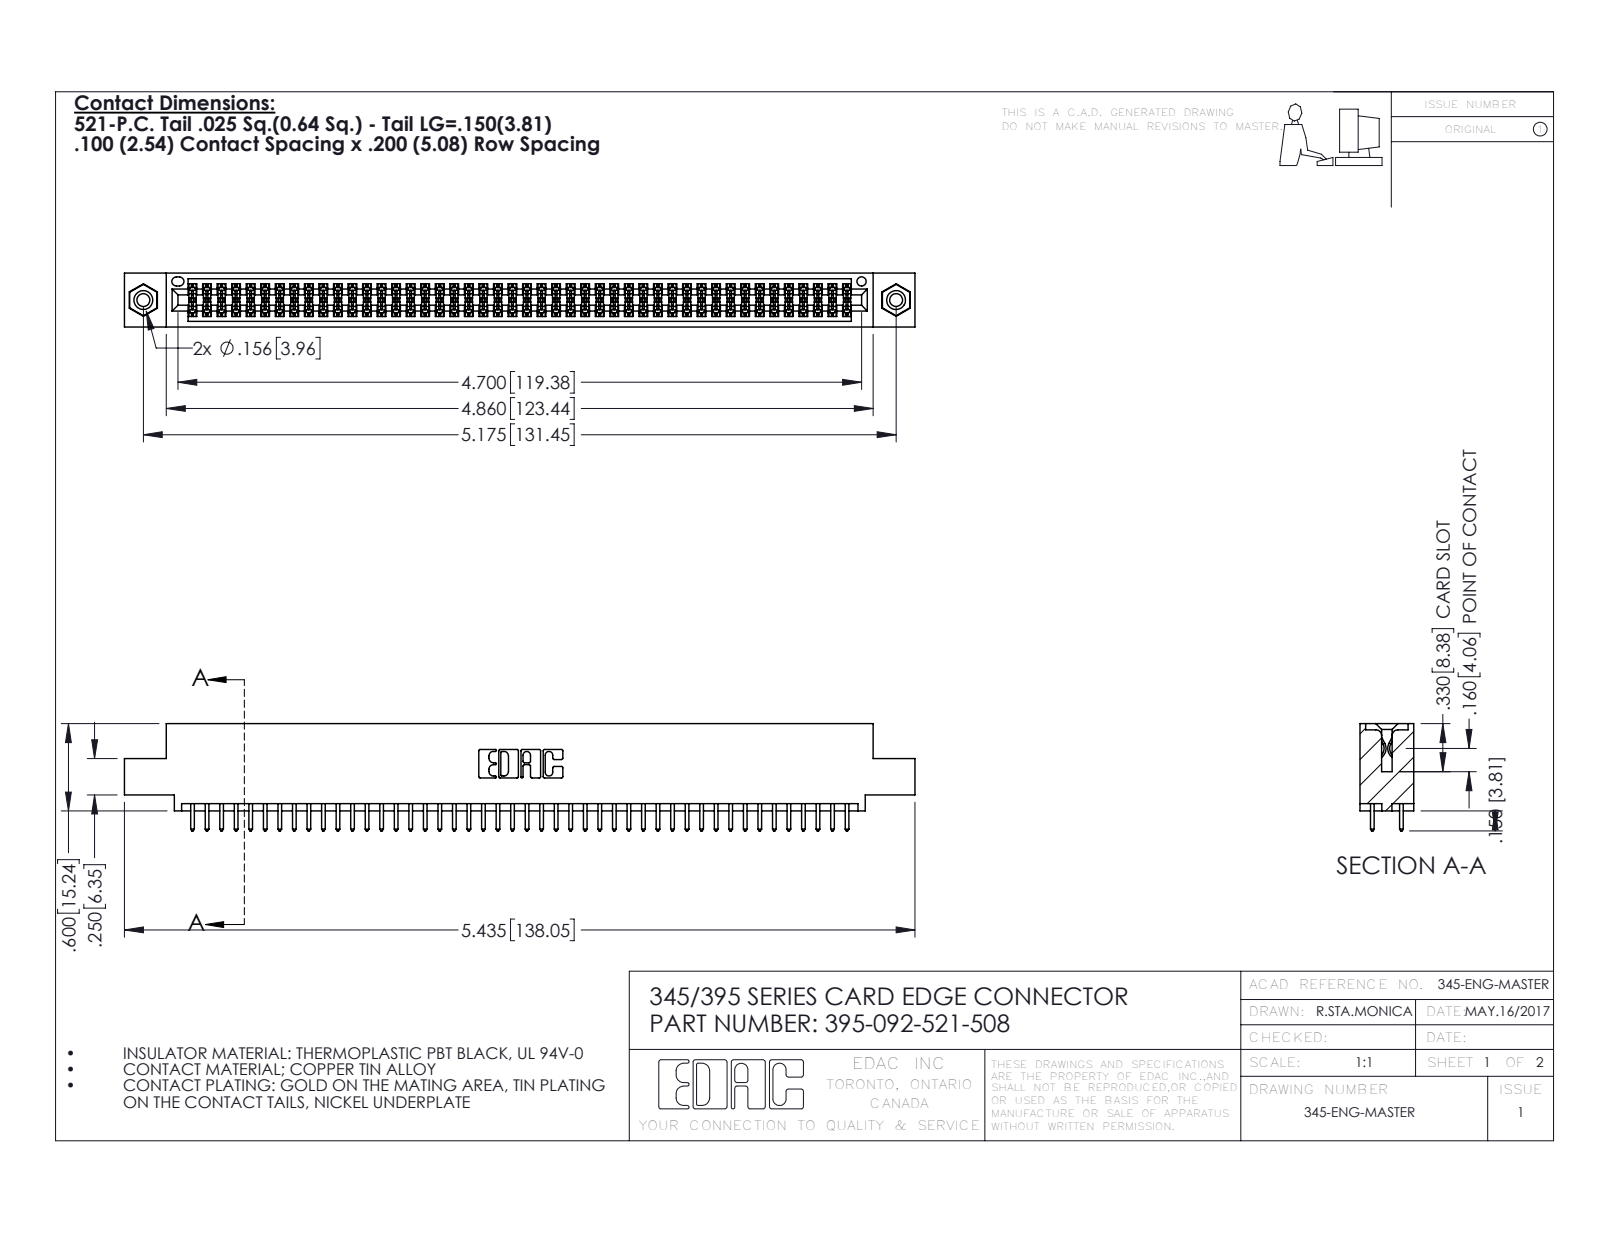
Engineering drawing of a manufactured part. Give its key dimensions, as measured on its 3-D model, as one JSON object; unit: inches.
{"part_name": "345-250-001_345-250-003-102; 345 Part_0.110 Offset - 0.156 Dia-TI; 395-092-521-508; 345-292-001_345-293-121", "step_written_by": "SolidWorks 2016 (CONFIG_CONTROL_DESIGN)", "units": "inches", "bodies": {"solids": 95, "faces": 4790, "planar": 3152, "cylindrical": 1622, "other": 16}, "overall_size": [5.435, 0.737, 0.37], "volume_in3": 0.813, "surface_area_in2": 30.45, "round_holes": [[0.089, 2], [0.125, 2], [0.156, 2], [0.064, 1]], "round_bosses_or_shafts": [[0.155, 2]], "partial_cylinders_radius": [[0.006, 138], [0.01, 92], [0.01, 22], [0.007, 6], [0.031, 6], [0.026, 3], [0.014, 2], [0.019, 2]], "face_to_face_distances": [0.072, 0.298, 0.2, 0.37, 0.098, 0.272, 0.025, 0.225, 0.175, 0.149], "hole_center_spacings": [0.27, 4.939, 5.175]}
